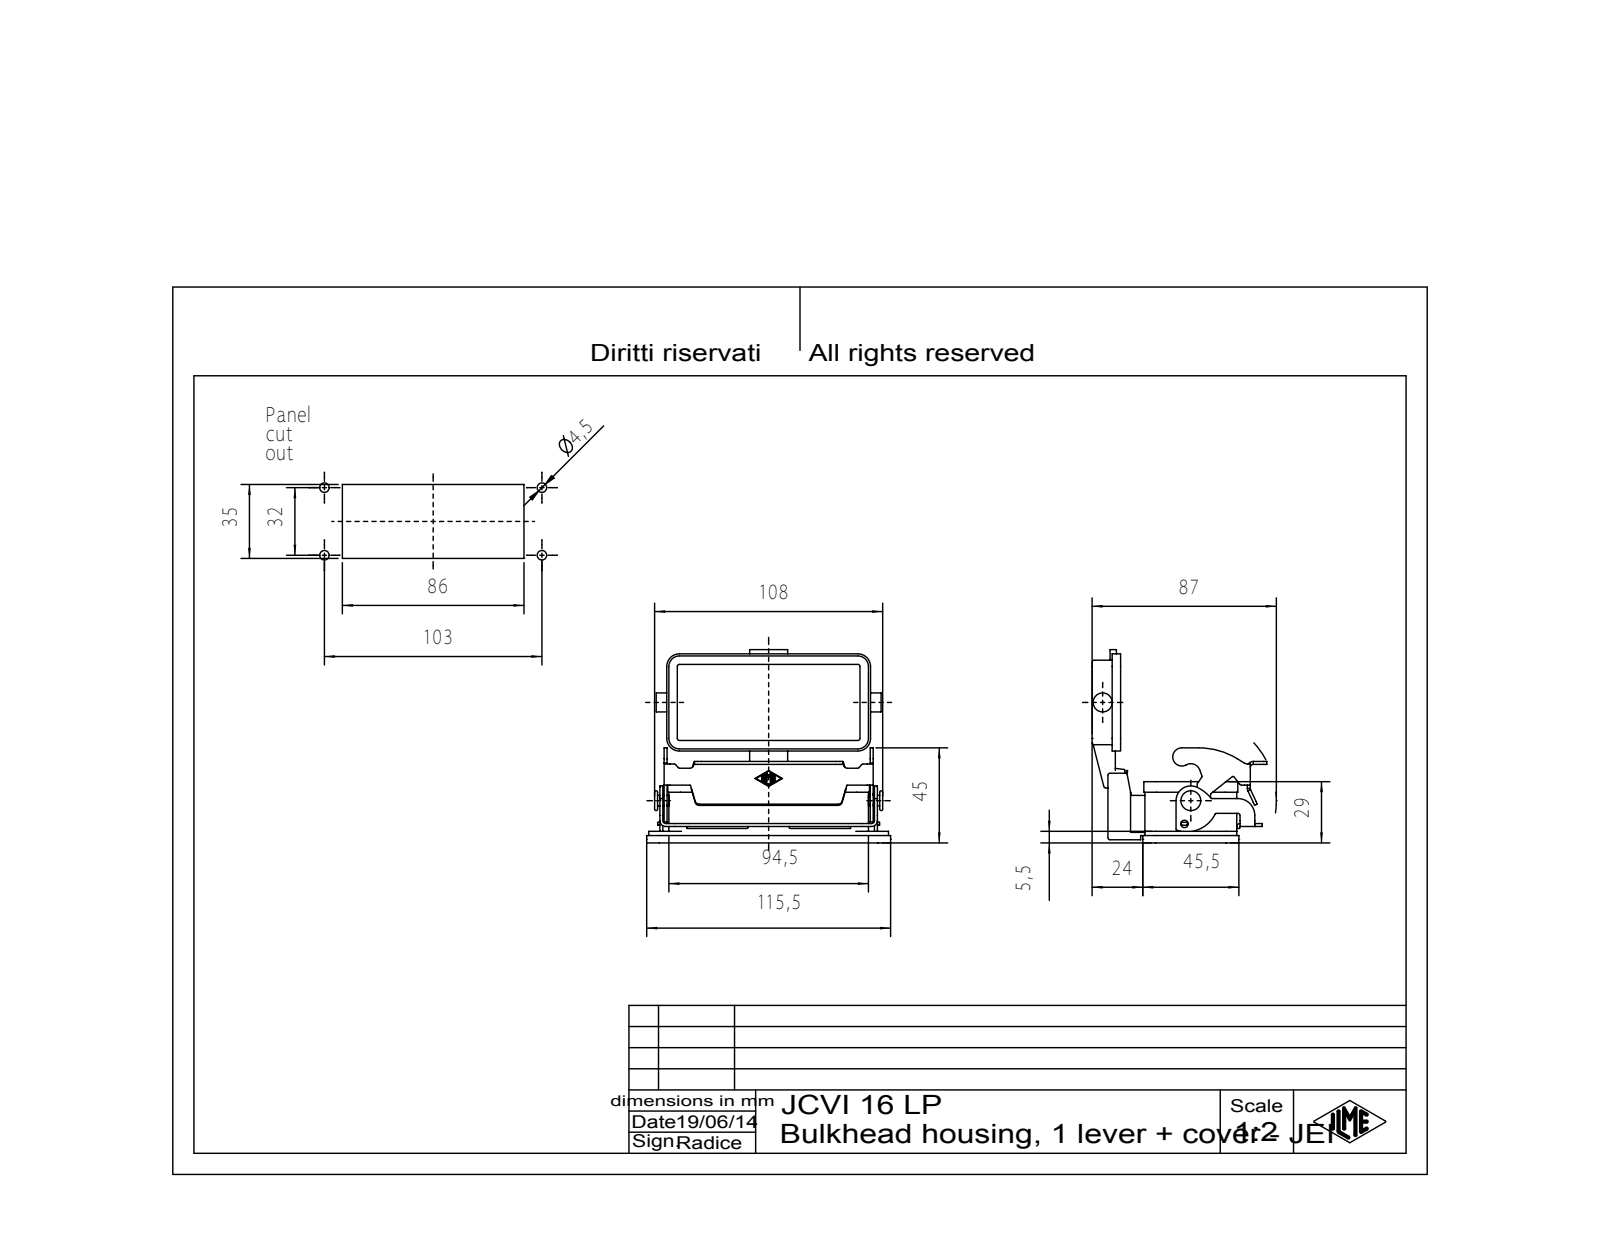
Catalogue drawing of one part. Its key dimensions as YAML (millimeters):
part_name: "JCVI_16_LP"
step_written_by: "Creo Elements/Direct Modeling 18.1F 24-Jul-2014 (C) Parametric Technology GmbH (AUTOMOTIVE_DESIGN)"
units: millimeters
bodies: {solids: 1, faces: 572, planar: 293, cylindrical: 241, other: 38}
overall_size: [115.5, 91.5, 82.73]
volume: 63613
surface_area: 54446
round_holes:
  - {diameter: 2.46, count: 4}
  - {diameter: 3, count: 4}
  - {diameter: 4.5, count: 4}
  - {diameter: 4.5, count: 4}
round_bosses_or_shafts:
  - {diameter: 9.1, count: 1}
  - {diameter: 7, count: 1}
  - {diameter: 5, count: 1}
  - {diameter: 4, count: 1}
  - {diameter: 3, count: 1}
partial_cylinders:
  - {radius: 1, count: 37}
  - {radius: 0.25, count: 16}
  - {radius: 3, count: 16}
  - {radius: 6, count: 16}
  - {radius: 0.5, count: 13}
  - {radius: 1.5, count: 11}
  - {radius: 2, count: 8}
  - {radius: 5, count: 8}
face_to_face_distances: [2, 1.4, 40.5, 3, 4, 0.5, 1.5, 41, 40, 3.5]
hole_center_spacings: [12.99, 32.14, 90.28, 94.95, 27, 32, 77.5, 82.07]
